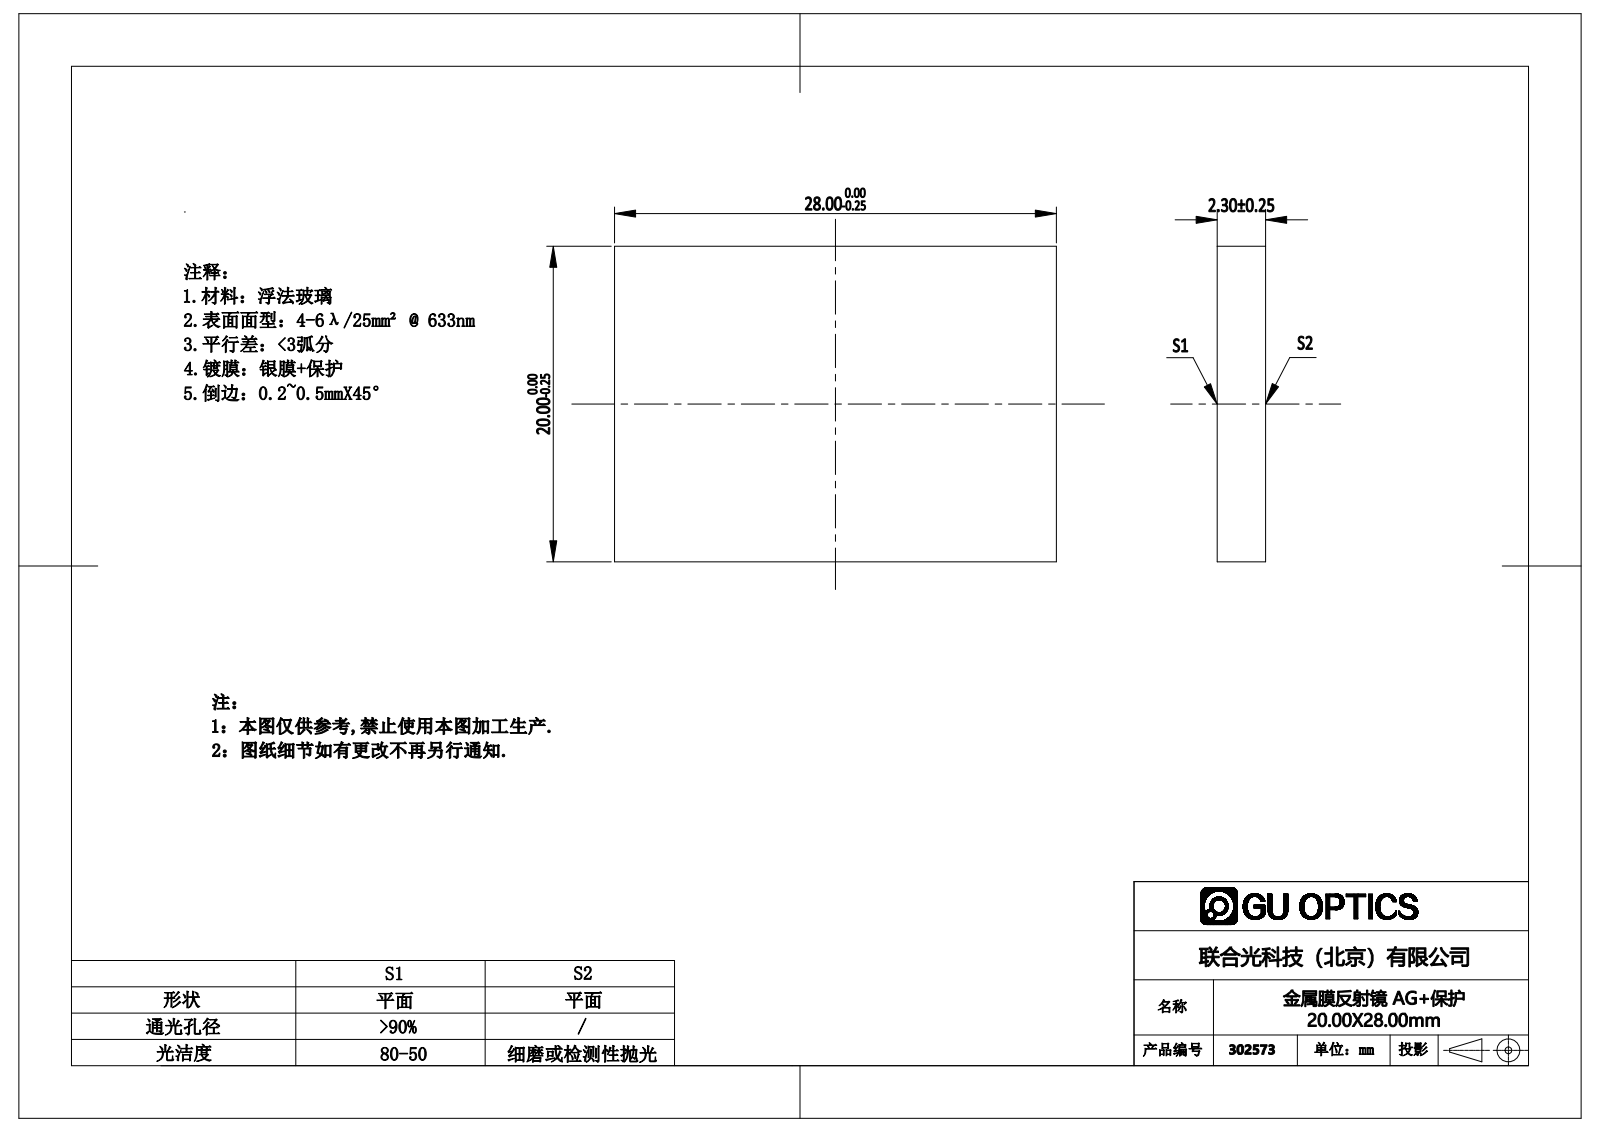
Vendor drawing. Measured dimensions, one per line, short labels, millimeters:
name: 302515
written by: SolidWorks 2016 (AUTOMOTIVE_DESIGN)
unit: mm
bodies: 1 solid, 6 faces (6 planar, 0 cylindrical, 0 other)
size: 21 × 15 × 2.3
volume: 724 mm³; area: 796 mm²
face distances: 2.3, 15, 21
